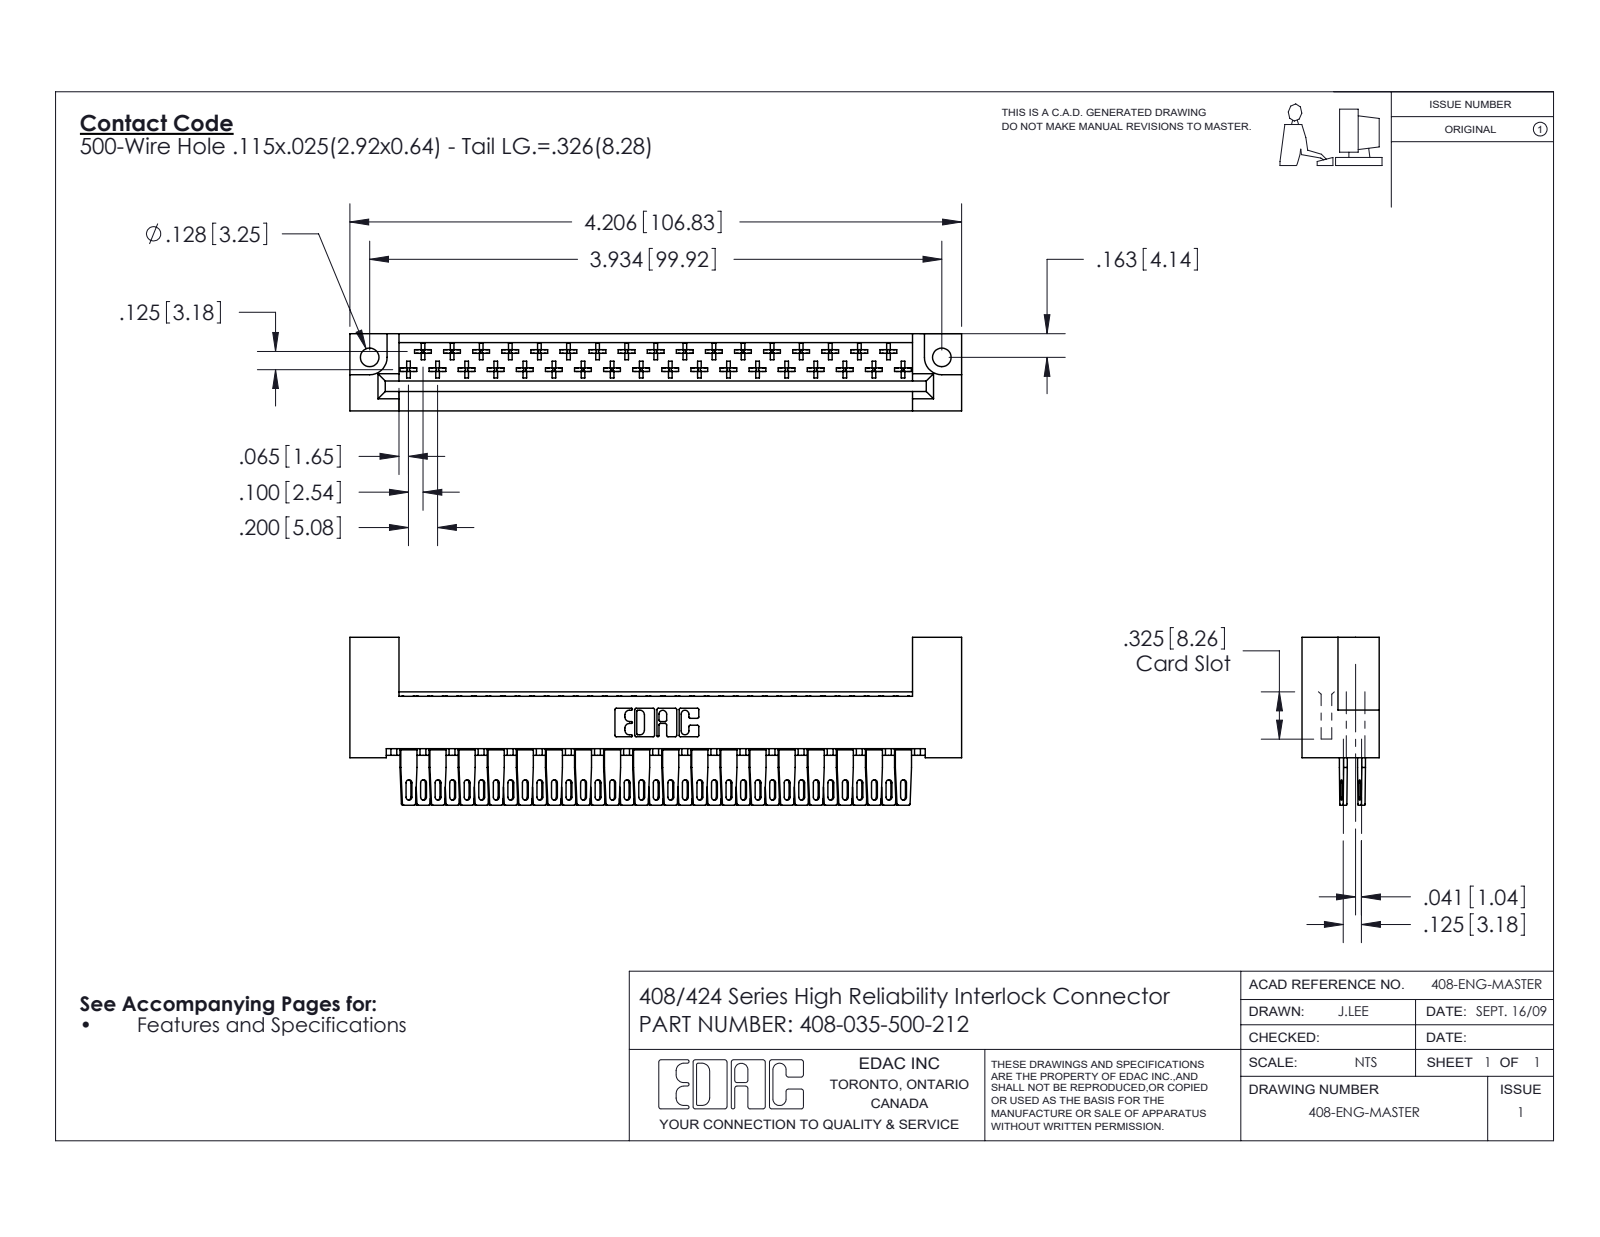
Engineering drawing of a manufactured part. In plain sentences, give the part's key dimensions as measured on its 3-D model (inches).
The part is named "408-035-500-212; 408-290-001_408-290-100; 408 Part_035 - 2". Its 3-D file was written by "SolidWorks 2016 (CONFIG_CONTROL_DESIGN)". It is 36 solids with 2134 faces: 1524 planar, 470 cylindrical and 140 other. Overall it measures 4.206 by 1.154 by 0.531 inches. Its volume is 0.834 cubic inches and its surface area 25.95 square inches. Round holes: 2 of diameter 0.128. Partial cylindrical surfaces (rounded edges, fillets, slot ends): 280 of radius 0.01, 70 of radius 0.021, 37 of radius 0.02, 22 of radius 0.01, 6 of radius 0.007, 6 of radius 0.031, 3 of radius 0.026, 2 of radius 0.12. The main face-to-face distances are 0.531, 0.125, 0.1, 0.025, 0.025, 0.361, 0.235, 0.259, 0.326, 0.217. The hole center spacings are 3.934.
